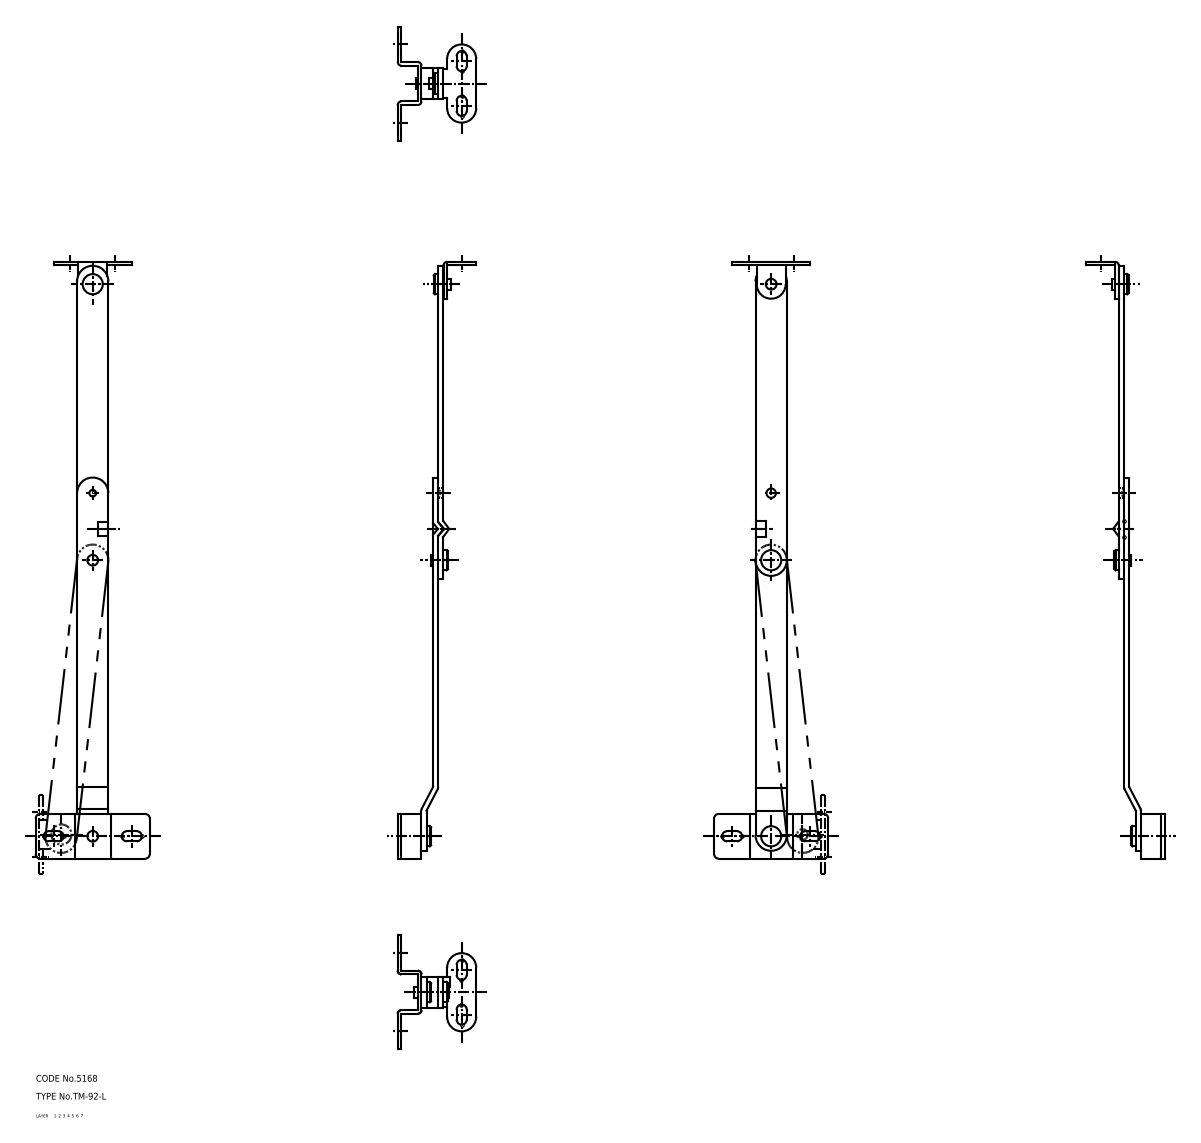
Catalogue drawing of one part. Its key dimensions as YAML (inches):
part_name: "rivet_2; rivet_1; bracket_B; bracket_A (+3 more)"
step_written_by: "CADfix (AUTOMOTIVE_DESIGN)"
units: inches
bodies: {solids: 7, faces: 133, planar: 0, cylindrical: 0, other: 133}
overall_size: [10.512, 2.008, 1.382]
volume: 0.807
surface_area: 23.73
